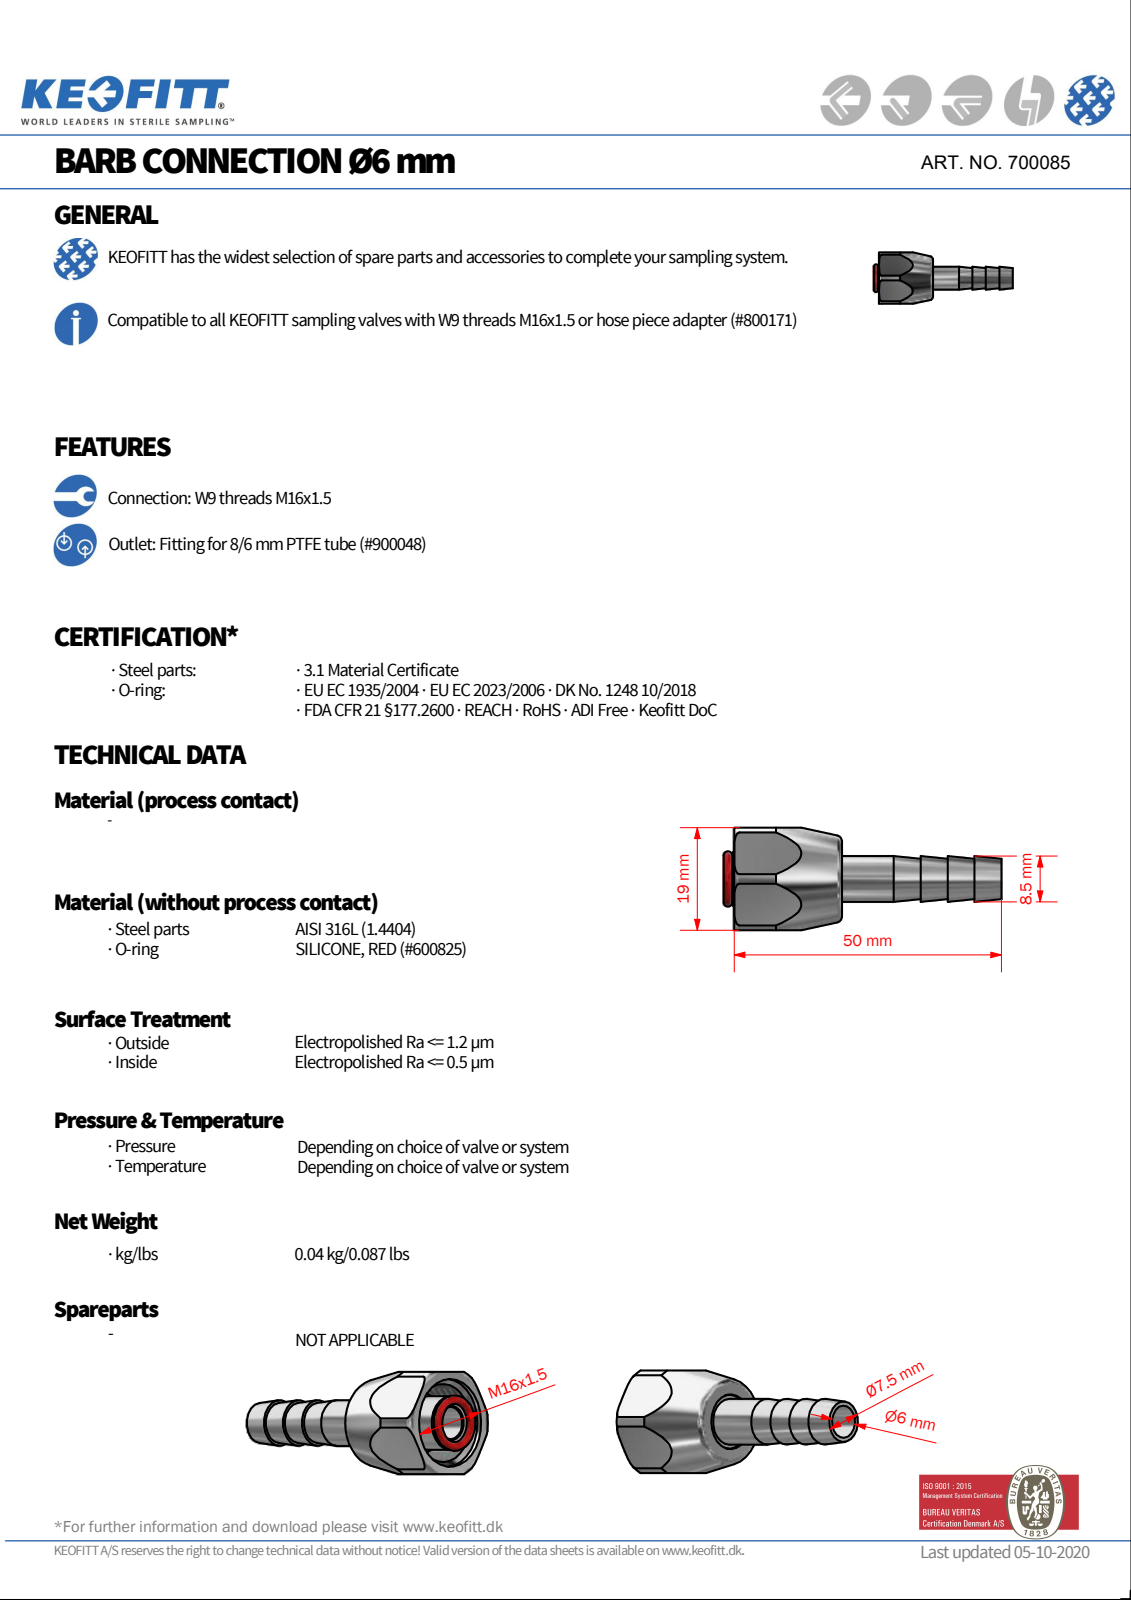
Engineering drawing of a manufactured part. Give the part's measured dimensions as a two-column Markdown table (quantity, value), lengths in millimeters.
| quantity | value |
| --- | --- |
| part name | 700085_simplify |
| STEP written by | Autodesk Inventor 2022 (AUTOMOTIVE_DESIGN) |
| units | millimeters |
| bodies | 2 solids, 37 faces (14 planar, 8 cylindrical, 15 other) |
| overall size | 51.6 × 21 × 19 |
| volume | 7 247 mm³ |
| surface area | 2 631 mm² |
| round bosses / shafts (diameter × count) | 10 × 1, 8.5 × 1 |
| partial cylindrical surfaces (radius × count) | 10.5 × 1 |
| main face-to-face distances | 19, 20, 20.37, 0.37, 29.63, 49.63, 50, 5, 10, 15 |
